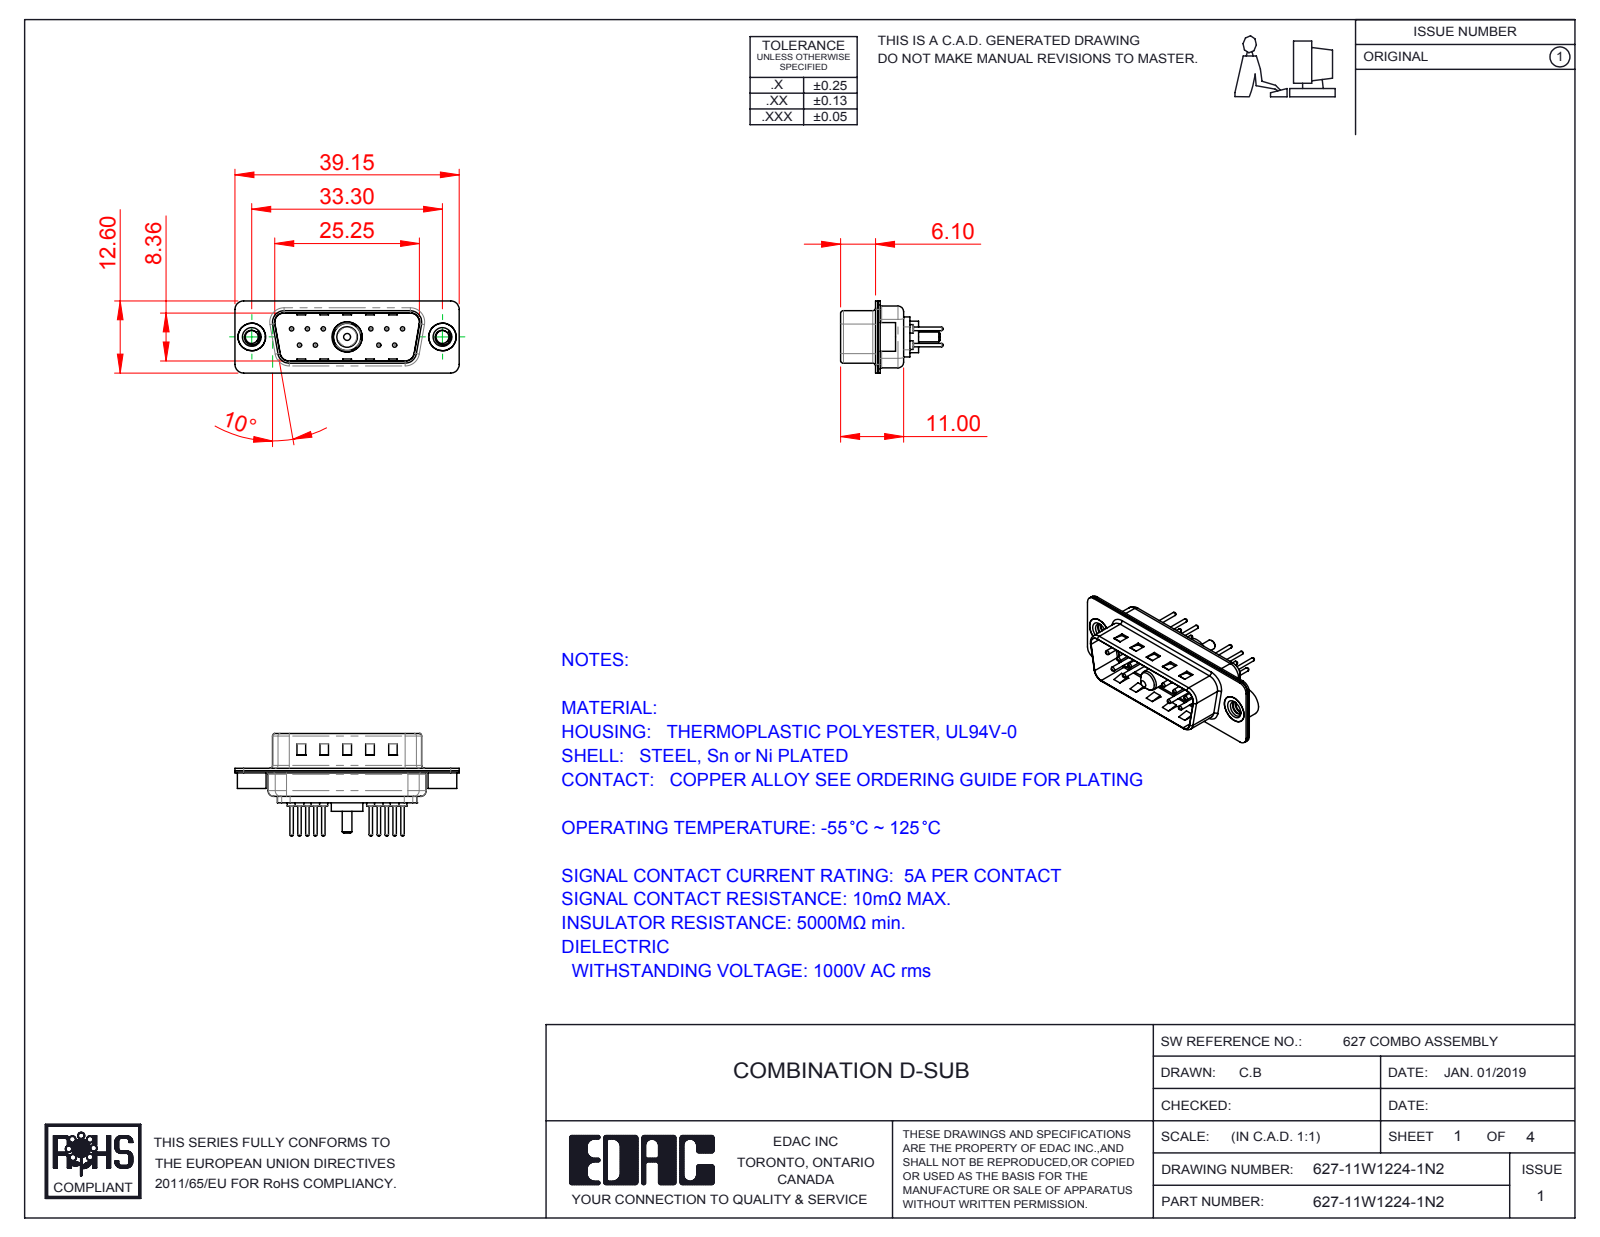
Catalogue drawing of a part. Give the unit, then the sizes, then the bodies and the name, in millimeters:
Units: millimetres
Overall size (bounding box): 39.15 × 17.9 × 12.6
Round holes (diameter × count): ⌀0.75 ×10, ⌀1.6 ×10, ⌀2 ×10, ⌀2.26 ×2, ⌀4 ×2, ⌀4.8 ×2, ⌀4.85 ×1, ⌀5.3 ×1
Round bosses / shafts (diameter × count): ⌀1.5 ×10, ⌀0.6 ×10, ⌀5 ×2, ⌀4.9 ×2, ⌀5.5 ×1, ⌀5.2 ×1, ⌀4.75 ×1, ⌀3.75 ×1
Partial cylindrical surfaces — rounded edges, fillets, slot ends (radius × count): R1.5 ×20, R2 ×12, R0.5 ×8, R1.6 ×8, R1 ×7, R0.25 ×4, R0.6 ×4, R0.65 ×4
Main face-to-face distances: 0.4, 0.82, 9.58, 8.76, 0.8, 1.5, 5.6, 1.4, 5.2, 6
Hole centre spacings: 3.16, 2.77, 13.85, 11.08, 16.62, 5.03, 5.04, 5.54
Volume: 1 897 mm³ · Surface area: 4 777 mm²
Bodies: 17 solids, 763 faces (228 planar, 296 cylindrical, 239 other)
Part name (STEP PRODUCT): Power Pin_10A S; 627Combo Threaded Rivet_2; 627Combo Shell Rear_15 Contacts; 627-11W1224-1N2 (+4 more)
STEP written by: SolidWorks 2016 (CONFIG_CONTROL_DESIGN)
